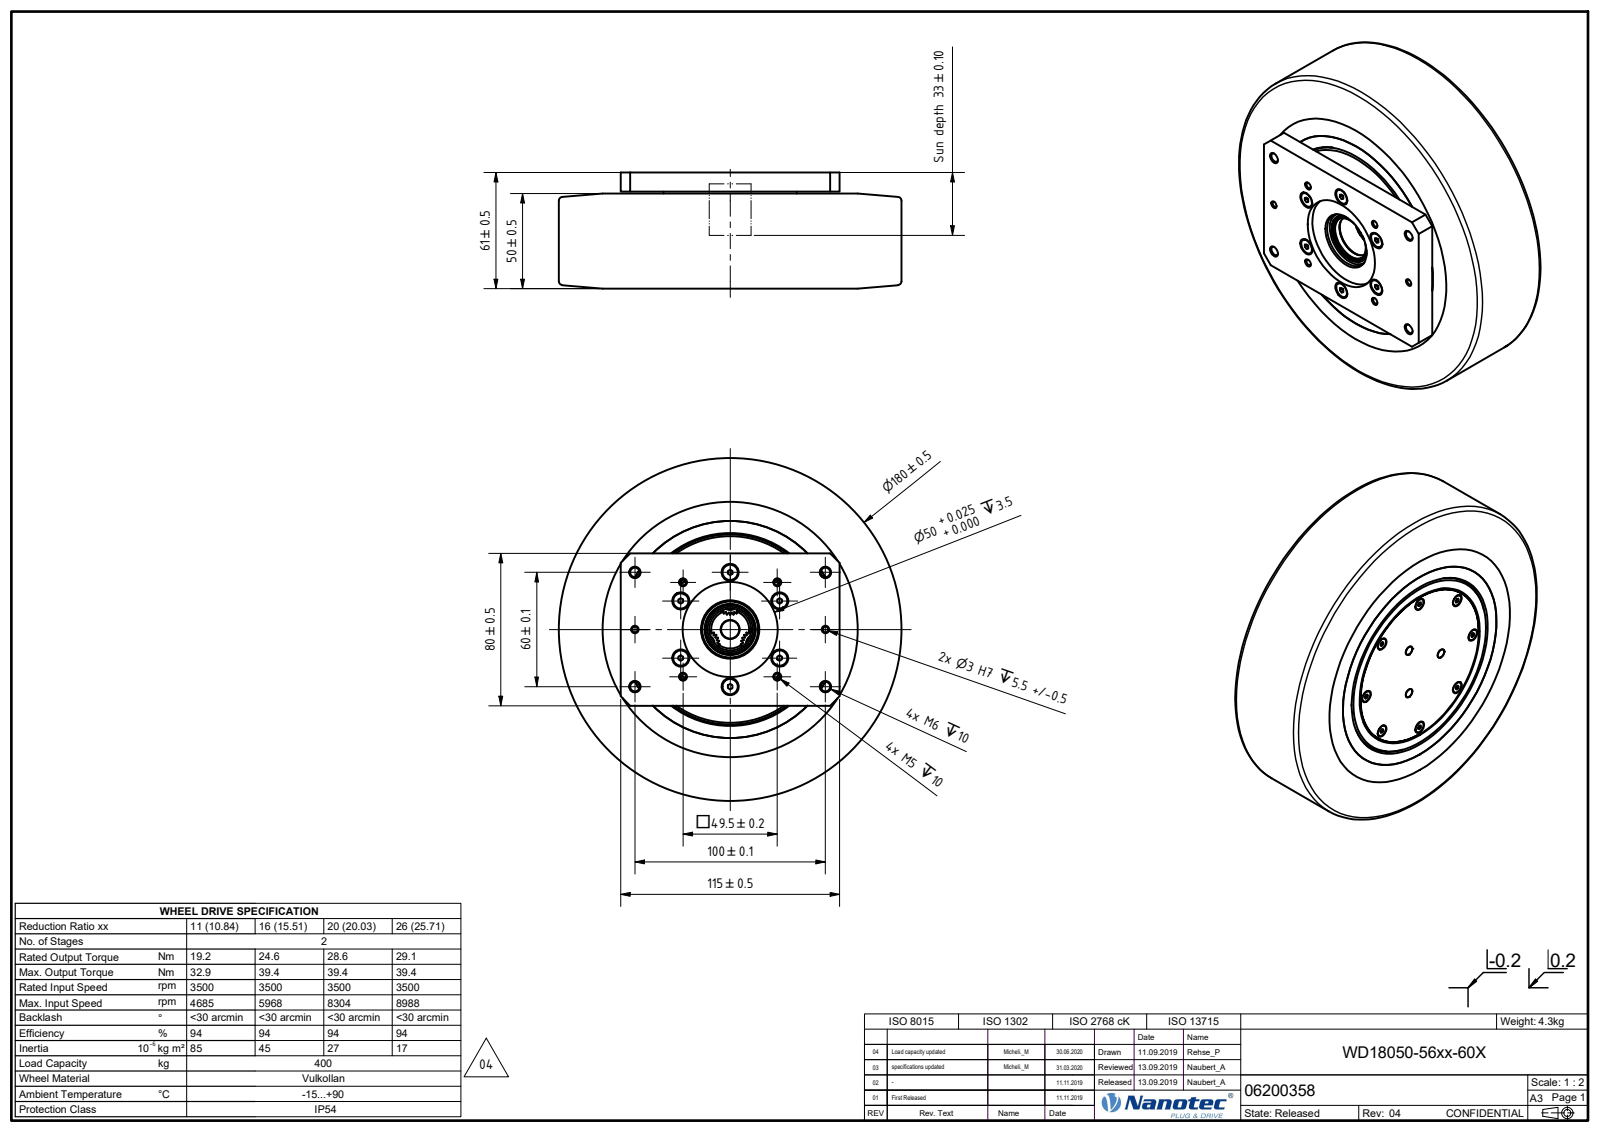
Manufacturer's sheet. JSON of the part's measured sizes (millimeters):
{"part_name": "D-00003074_Shrinkwrap_1", "step_written_by": "Autodesk Inventor 2018 (AUTOMOTIVE_DESIGN)", "units": "millimeters", "bodies": {"solids": 1, "faces": 210, "planar": 137, "cylindrical": 33, "other": 40}, "overall_size": [180, 180, 61], "volume_mm3": 1348000, "surface_area_mm2": 95441, "round_holes": [[4.92, 8], [4.97, 3], [3, 2], [30, 1], [50, 1]], "round_bosses_or_shafts": [[6, 8], [8, 6], [180, 1], [100, 1], [88, 1], [70, 1]], "face_to_face_distances": [50, 61, 11, 1, 10, 51, 6.5, 5.5, 3.5, 57.5], "hole_center_spacings": [25.79, 30, 35, 35.36, 49.5, 58.31, 60.29, 74.93]}
